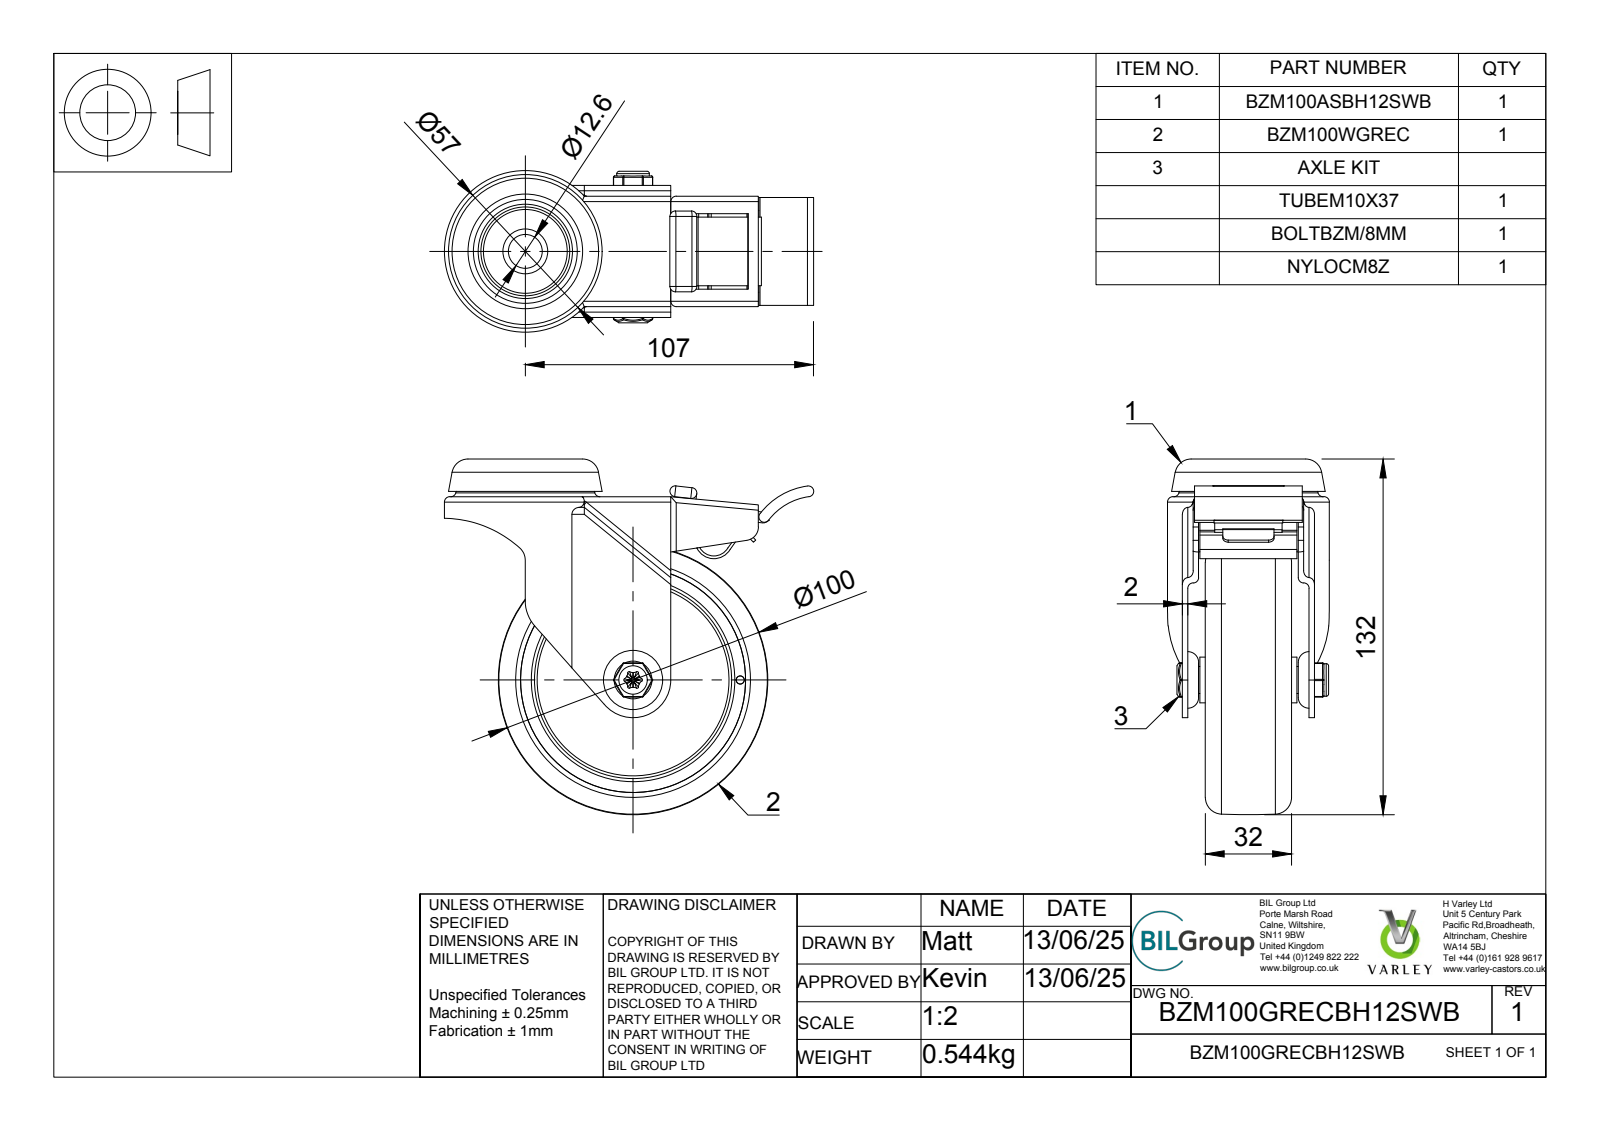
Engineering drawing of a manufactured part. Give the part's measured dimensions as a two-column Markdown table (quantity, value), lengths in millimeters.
| quantity | value |
| --- | --- |
| part name | BZM100GRECBH12SWB v3; BZM100ASBH12SWB v1; ZINC PLATED PRESSED STEEL HEAD; ZINC PLATED PRESSED STEEL FORKS (+8 more) |
| STEP written by | Autodesk Translation Framework v13.20.0.188 (AP242_MANAGED_MODEL_BASED_3D_ENGINEERING_MIM_LF) |
| units | millimeters |
| bodies | 12 solids, 488 faces (210 planar, 174 cylindrical, 104 other) |
| overall size | 137 × 132 × 60 |
| volume | 203 969 mm³ |
| surface area | 106 046 mm² |
| round holes (diameter × count) | 3 × 1, 8 × 1, 8.2 × 1, 8.3 × 1, 8.6 × 1, 10.1 × 1, 10.3 × 1, 12.6 × 1, 83.5 × 1 |
| round bosses / shafts (diameter × count) | 48 × 1, 30 × 1, 17 × 1, 12.1 × 1, 10 × 1, 7.87 × 1, 6.45 × 1 |
| partial cylindrical surfaces (radius × count) | 2 × 40, 0.5 × 24, 1 × 11, 6 × 5, 1.5 × 2, 3 × 2, 5 × 2, 14 × 2 |
| main face-to-face distances | 2, 6, 4, 21.5, 43, 41, 2.5, 27.5, 19, 40.5 |
| hole center spacings | 39.75 |
